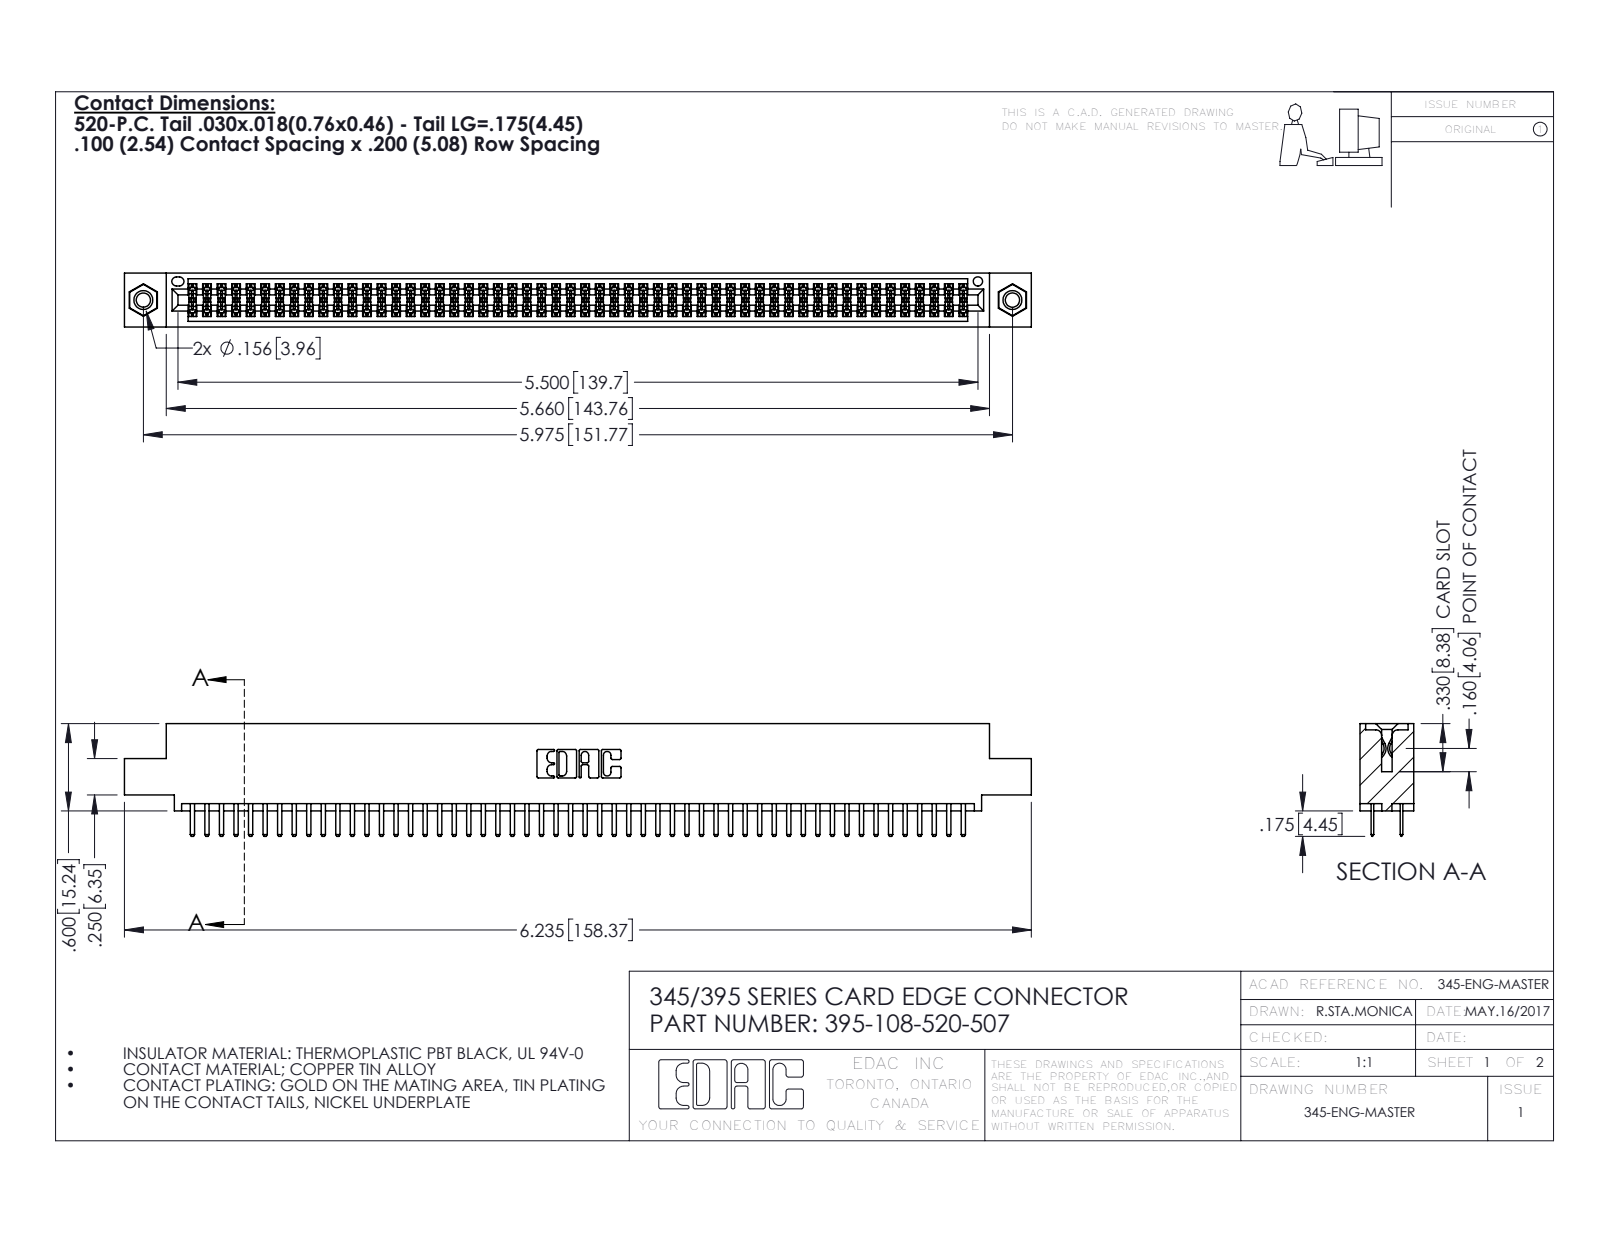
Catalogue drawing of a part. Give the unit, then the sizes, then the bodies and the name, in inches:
Units: inches
Overall size (bounding box): 6.235 × 0.775 × 0.37
Round holes (diameter × count): ⌀0.098 ×2, ⌀0.125 ×2, ⌀0.156 ×2, ⌀0.064 ×1
Round bosses / shafts (diameter × count): ⌀0.155 ×2
Partial cylindrical surfaces — rounded edges, fillets, slot ends (radius × count): R0.006 ×162, R0.01 ×112, R0.01 ×22, R0.007 ×6, R0.031 ×6, R0.026 ×3, R0.014 ×2, R0.019 ×2
Main face-to-face distances: 0.072, 0.298, 0.2, 0.37, 0.098, 0.272, 0.025, 0.225, 0.022, 0.072
Hole centre spacings: 0.27, 5.739, 5.975
Volume: 0.937 in³ · Surface area: 35.59 in²
Bodies: 111 solids, 6022 faces (3896 planar, 2110 cylindrical, 16 other)
Part name (STEP PRODUCT): 345-250-001_345-250-005-103; 345 Part_0.110 Offset - 0.156 Dia-TI; 395-108-520-507; 345-292-001_345-293-120
STEP written by: SolidWorks 2016 (CONFIG_CONTROL_DESIGN)
